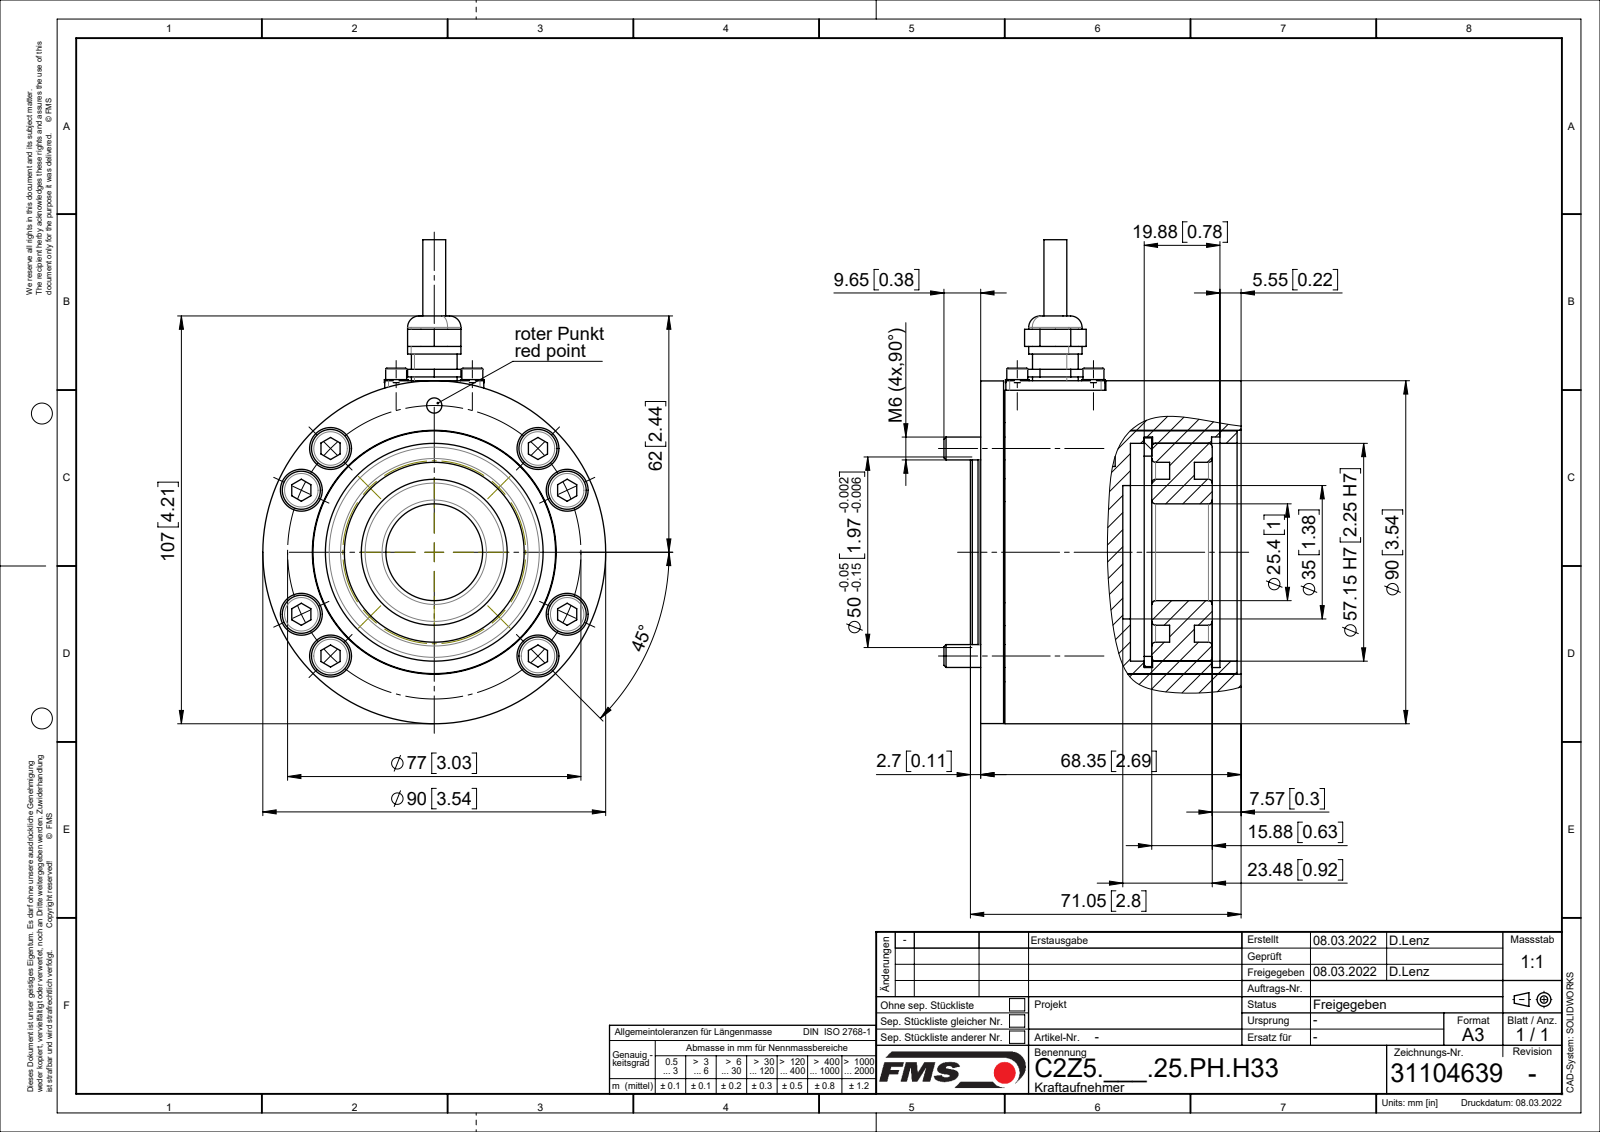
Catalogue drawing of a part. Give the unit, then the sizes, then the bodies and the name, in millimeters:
Units: millimetres
Overall size (bounding box): 127 × 90 × 78
Round holes (diameter × count): ⌀6.5 ×8, ⌀11 ×8, ⌀2.5 ×6, ⌀3.1 ×4, ⌀3.4 ×4, ⌀5 ×4, ⌀7 ×4, ⌀4 ×2, ⌀6 ×1, ⌀10.2 ×1, ⌀12.2 ×1, ⌀18 ×1
Round bosses / shafts (diameter × count): ⌀10 ×8, ⌀6 ×8, ⌀6.2 ×4, ⌀5.5 ×4, ⌀3 ×4, ⌀90 ×1, ⌀89.9 ×1, ⌀63.7 ×1
Partial cylindrical surfaces — rounded edges, fillets, slot ends (radius × count): R0.1 ×4, R1 ×4, R4.16 ×2, R5 ×2, R23.2 ×1, R26.29 ×1
Main face-to-face distances: 6, 3.3, 2.7, 33.05, 32, 38, 30, 29.3, 35.3, 28.95
Hole centre spacings: 20, 38.5, 13.37, 14.14, 38.49, 44.16, 54.44, 63.07
Volume: 296 468 mm³ · Surface area: 118 599 mm²
Bodies: 24 solids, 556 faces (222 planar, 232 cylindrical, 102 other)
Part name (STEP PRODUCT): Zyl-Schr DIN912_M6x30; 31104502_01; 31101749_01; 31104496_stp_01 (+8 more)
STEP written by: SolidWorks 2018 (CONFIG_CONTROL_DESIGN)
